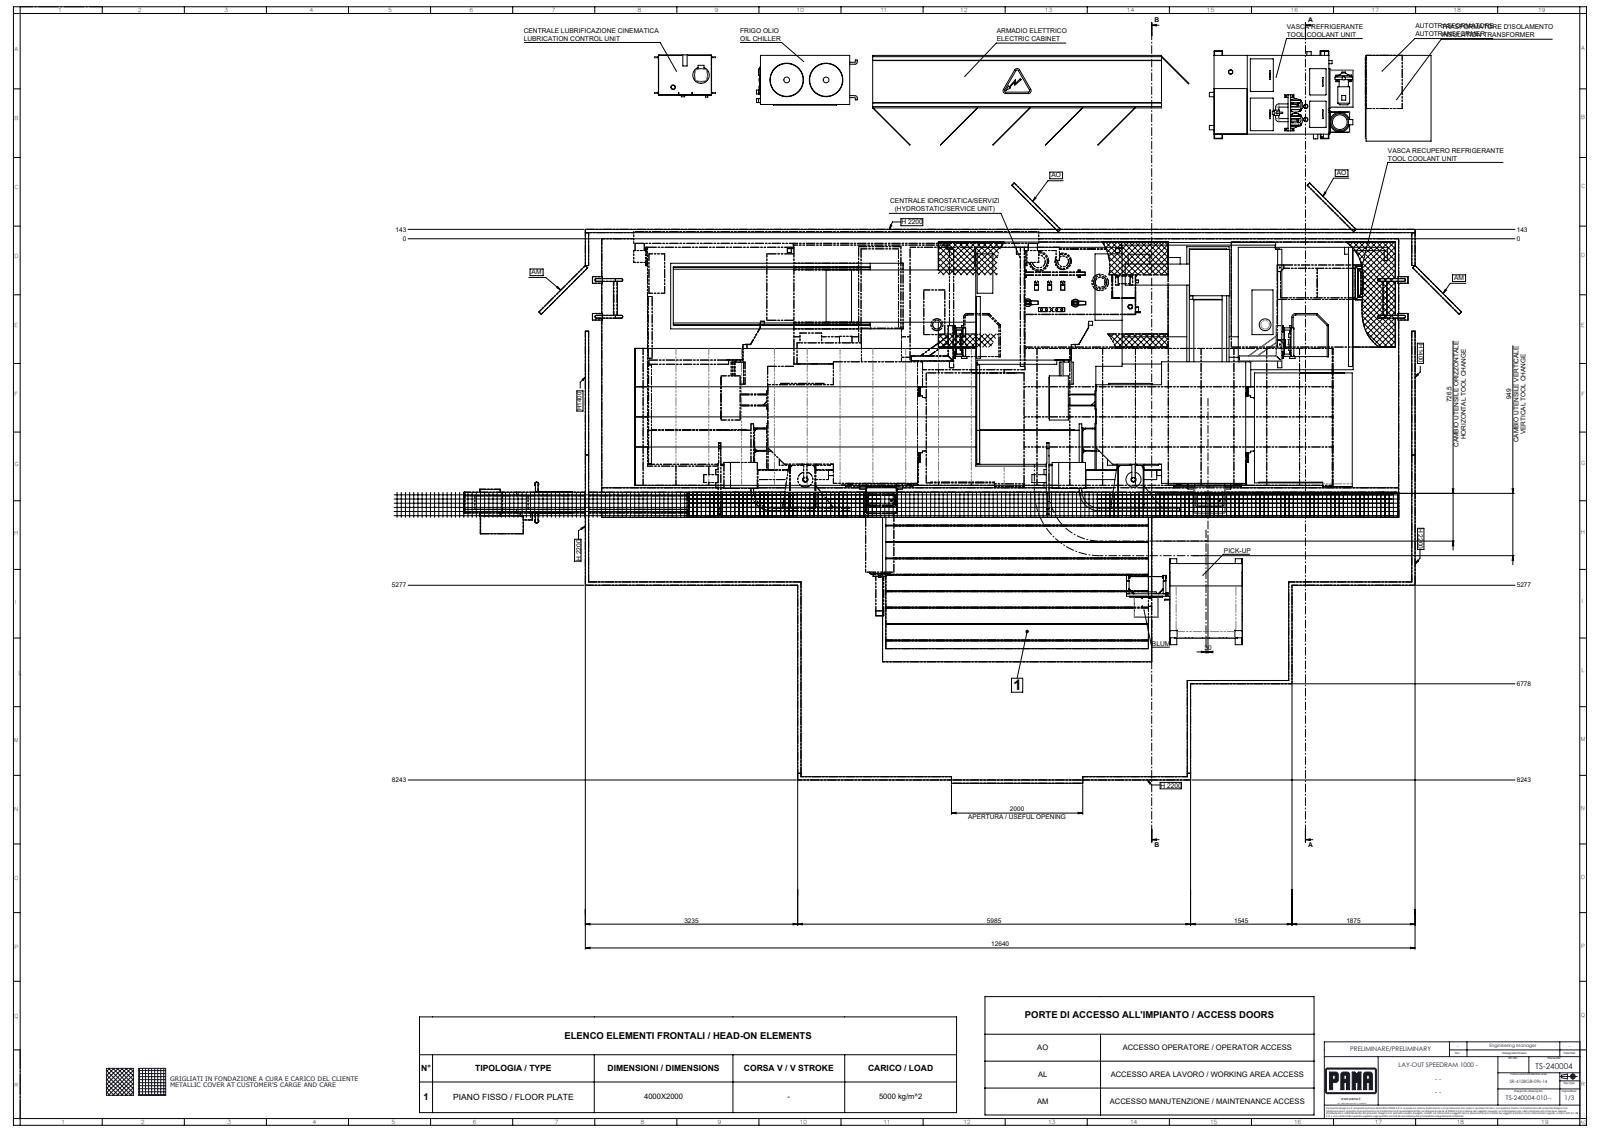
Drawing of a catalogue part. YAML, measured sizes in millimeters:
part_name: "S001568_1000 L; S002410; S001560_6 (5+1) POSTI (SINGOLA COLONNA); S003261_ISO 50 - RIPOSO (+8 more)"
step_written_by: "SolidWorks 2023 (AUTOMOTIVE_DESIGN)"
units: millimeters
bodies: {solids: 569, faces: 9744, planar: 6689, cylindrical: 2433, other: 622}
overall_size: [25140, 18167.4, 11449]
volume: 778100000000
surface_area: 2857000000
round_holes:
  - {diameter: 35, count: 188}
  - {diameter: 69.6, count: 103}
  - {diameter: 37.2, count: 18}
  - {diameter: 5, count: 17}
  - {diameter: 7, count: 9}
  - {diameter: 30, count: 9}
  - {diameter: 13, count: 8}
  - {diameter: 14, count: 8}
  - {diameter: 11, count: 7}
  - {diameter: 8, count: 6}
  - {diameter: 340, count: 5}
  - {diameter: 6.6, count: 4}
round_bosses_or_shafts:
  - {diameter: 42.4, count: 18}
  - {diameter: 20, count: 15}
  - {diameter: 40, count: 11}
  - {diameter: 150, count: 10}
  - {diameter: 9, count: 10}
  - {diameter: 60, count: 9}
  - {diameter: 55, count: 8}
  - {diameter: 66.3, count: 7}
partial_cylinders:
  - {radius: 5, count: 224}
  - {radius: 15, count: 97}
  - {radius: 35, count: 62}
  - {radius: 8, count: 52}
  - {radius: 10, count: 40}
  - {radius: 20, count: 36}
  - {radius: 6, count: 31}
  - {radius: 3, count: 25}
face_to_face_distances: [2000, 50, 720, 1280, 10, 447, 12446, 18096, 1167, 833]
hole_center_spacings: [273.13, 500, 1431.99, 758.02, 1597.06, 1000, 1254.83, 1884.3]
